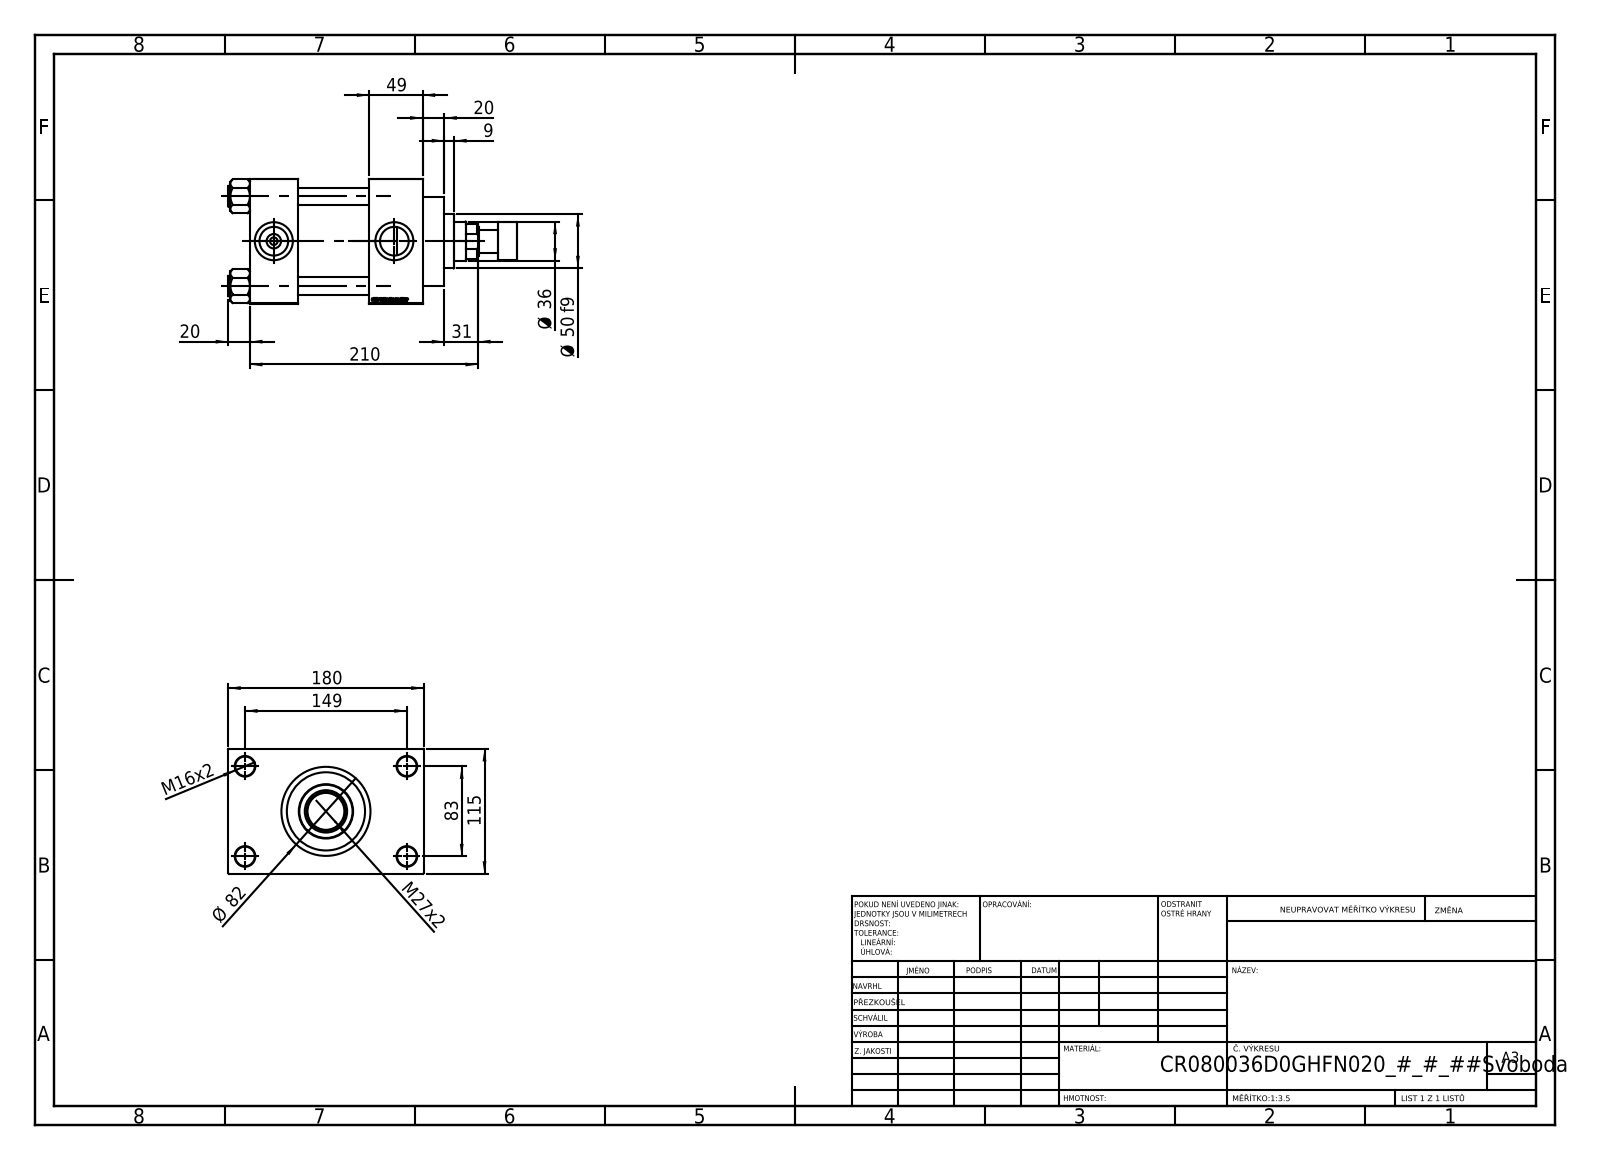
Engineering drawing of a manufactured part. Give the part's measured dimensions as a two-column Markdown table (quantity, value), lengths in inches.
| quantity | value |
| --- | --- |
| part name | V215CR_VCP_D; V215_VC_A; NUT_M5_D; V215CR_D_TYCINKA (+2 more) |
| STEP written by | SolidWorks 2019 (CONFIG_CONTROL_DESIGN) |
| units | inches |
| bodies | 12 solids, 1165 faces (549 planar, 92 cylindrical, 524 other) |
| overall size | 10.472 × 7.087 × 4.528 |
| volume | 122.2 in³ |
| surface area | 468.4 in² |
| round holes (diameter × count) | 0.63 × 4, 0.709 × 4, 0.276 × 2, 1.041 × 2, 1.378 × 2, 1.004 × 1, 1.417 × 1, 1.535 × 1, 2.402 × 1, 2.835 × 1, 3.15 × 1 |
| round bosses / shafts (diameter × count) | 0.748 × 4, 3.386 × 1, 3.228 × 1, 1.969 × 1, 1.378 × 1, 0.827 × 1 |
| main face-to-face distances | 4.528, 2.598, 1.929, 4.331, 1.732, 6.26, 1.28, 5.807, 0.787, 2.717 |
| hole center spacings | 1.305, 2.302, 3.256, 3.357, 3.513, 4.561, 5.607, 3.268 |
